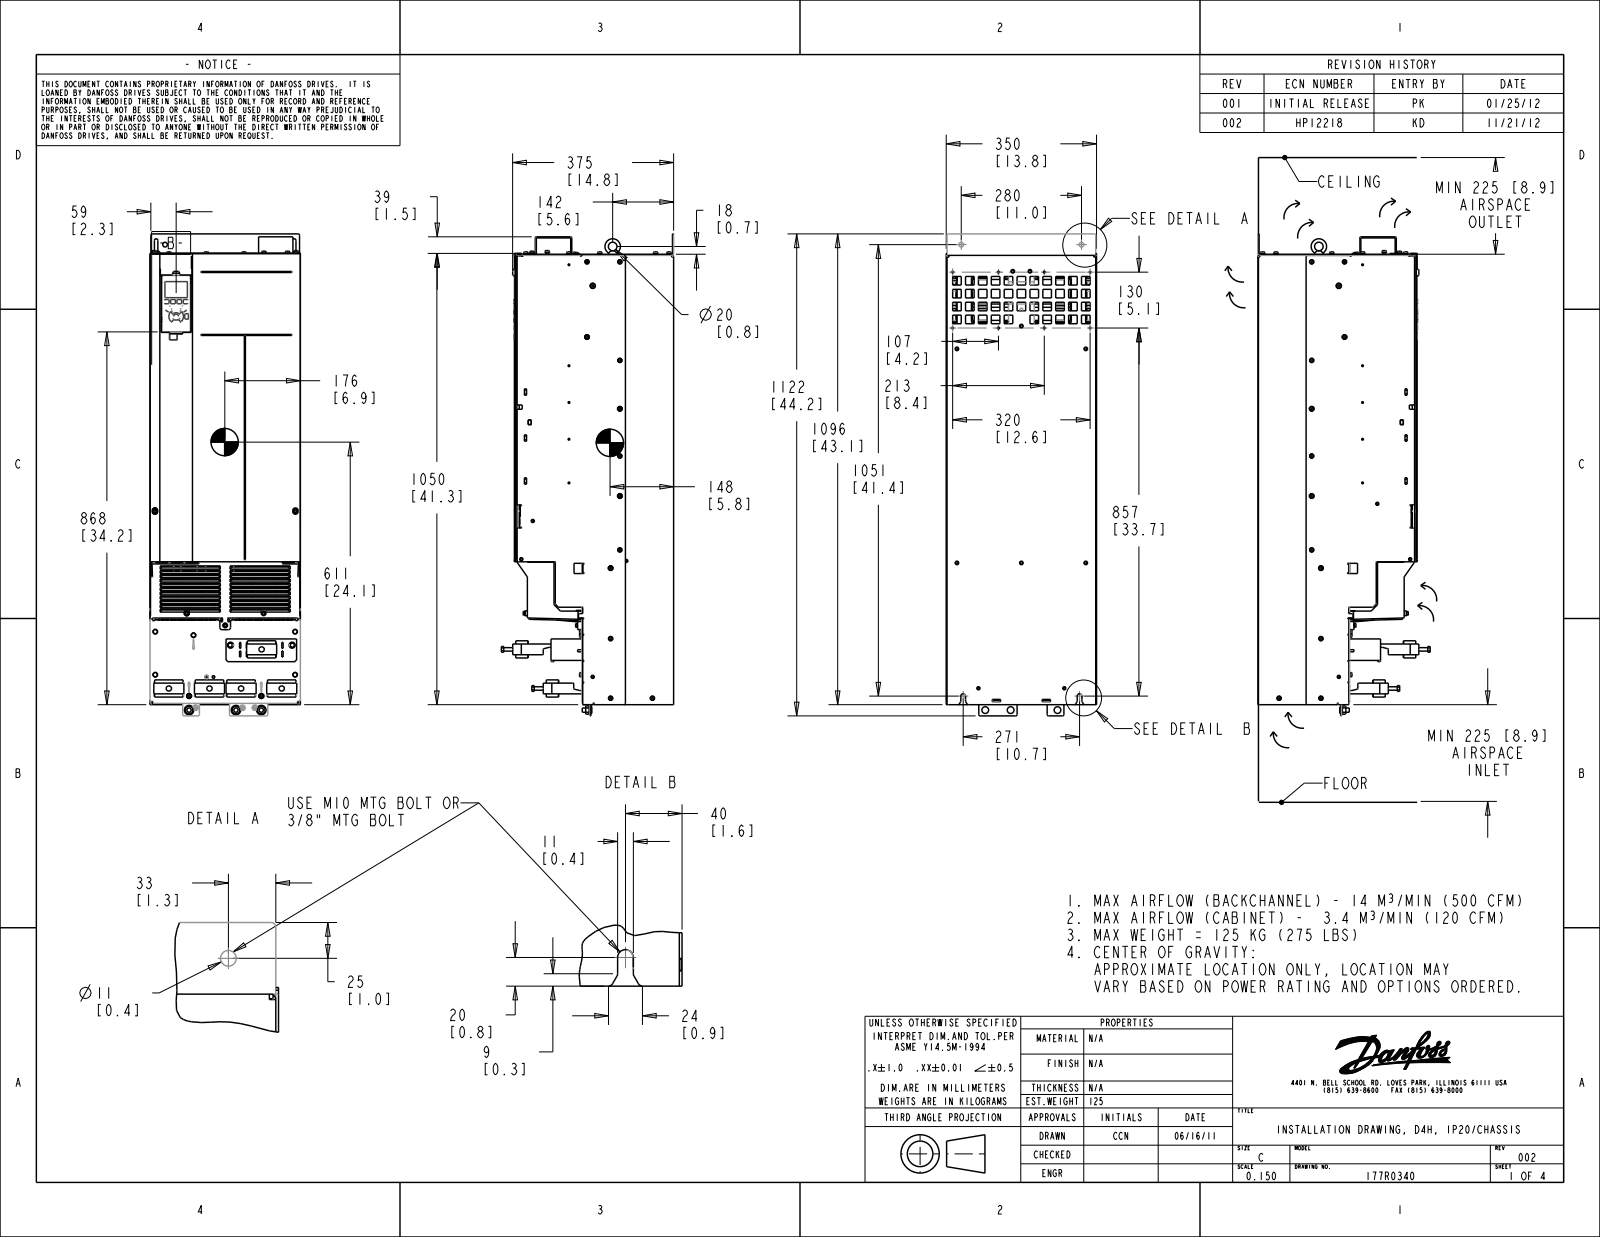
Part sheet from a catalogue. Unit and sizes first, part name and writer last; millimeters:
Units: millimetres
Overall size (bounding box): 1122.68 × 374.88 × 350
Round holes (diameter × count): ⌀5 ×50, ⌀4.2 ×49, ⌀6 ×29, ⌀4 ×17, ⌀6.4 ×15, ⌀6.5 ×13, ⌀4.75 ×12, ⌀6.35 ×11, ⌀4.5 ×9, ⌀5.5 ×9, ⌀10 ×9, ⌀3.4 ×8
Round bosses / shafts (diameter × count): ⌀8 ×44, ⌀5 ×42, ⌀8.7 ×26, ⌀6.33 ×26, ⌀10.8 ×20, ⌀9.8 ×20, ⌀7.4 ×15, ⌀11 ×11
Partial cylindrical surfaces — rounded edges, fillets, slot ends (radius × count): R1.5 ×624, R0.5 ×412, R3.2 ×392, R0.25 ×258, R4 ×184, R1 ×97, R1.18 ×72, R0.2 ×71
Main face-to-face distances: 1.9, 346.2, 348.1, 3.8, 344.3, 211.6, 350, 368.5, 366.6, 364.9
Hole centre spacings: 130, 168.16, 106.67, 213.33, 249.82, 120, 134.3, 300
Volume: 6 037 000 mm³ · Surface area: 5 194 000 mm²
Bodies: 212 solids, 20325 faces (13048 planar, 4608 cylindrical, 2669 other)
Part name (STEP PRODUCT): 177G3904; FH-M6-12-ZI; S-M8-1-ZI; TPS-5MM-16 (+8 more)
STEP written by: CREO PARAMETRIC BY PTC INC, 2015480 (CONFIG_CONTROL_DESIGN)
